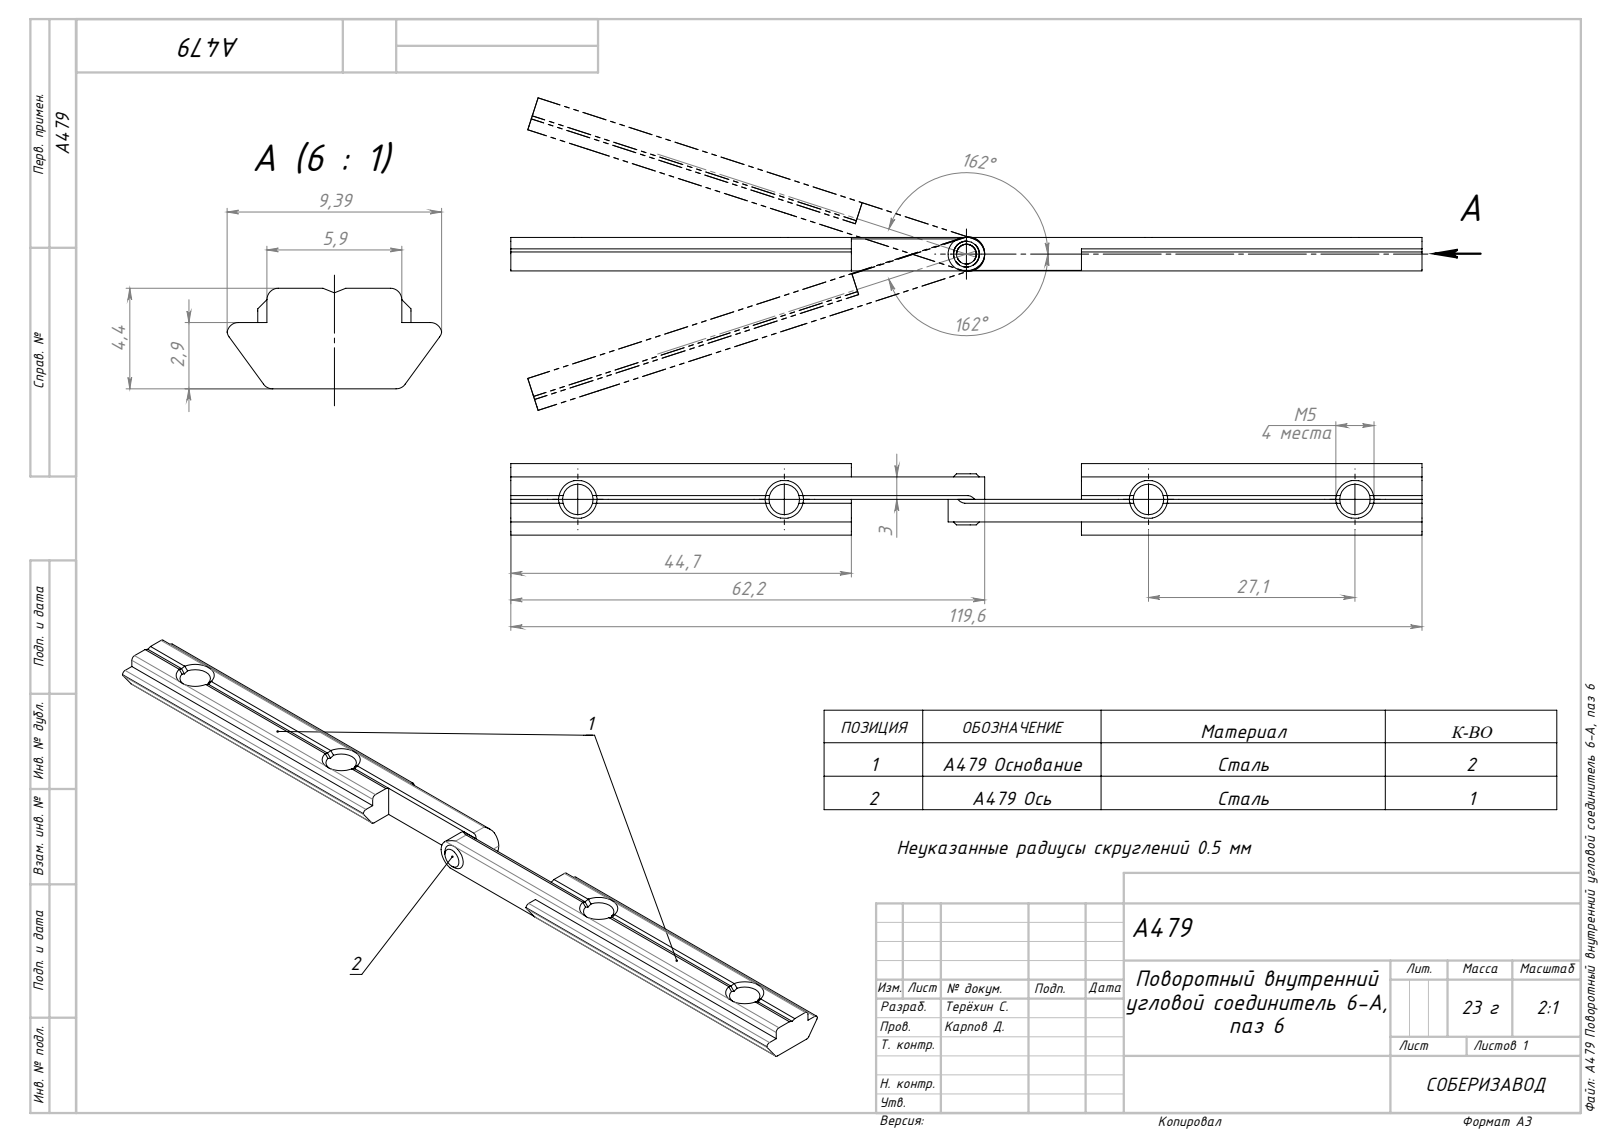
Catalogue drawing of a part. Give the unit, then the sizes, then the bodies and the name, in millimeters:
Units: millimetres
Overall size (bounding box): 119.6 × 9.39 × 4.4
Round holes (diameter × count): ⌀4 ×4, ⌀3 ×1
Partial cylindrical surfaces — rounded edges, fillets, slot ends (radius × count): R0.5 ×8, R2.2 ×2
Main face-to-face distances: 4.4, 2.95, 2.9, 1.5, 5.9, 44.7, 74.9, 119.6, 30.2, 0.4
Hole centre spacings: 27.1, 74.9, 47.8, 102
Volume: 3 033 mm³ · Surface area: 2 986 mm²
Bodies: 3 solids, 124 faces (50 planar, 34 cylindrical, 40 other)
Part name (STEP PRODUCT): A479 Ось_00; A479 Основание_00; A479 Поворотный внутренний угловой соединитель 6-А, паз 6
STEP written by: SolidWorks 2021 (AUTOMOTIVE_DESIGN)
